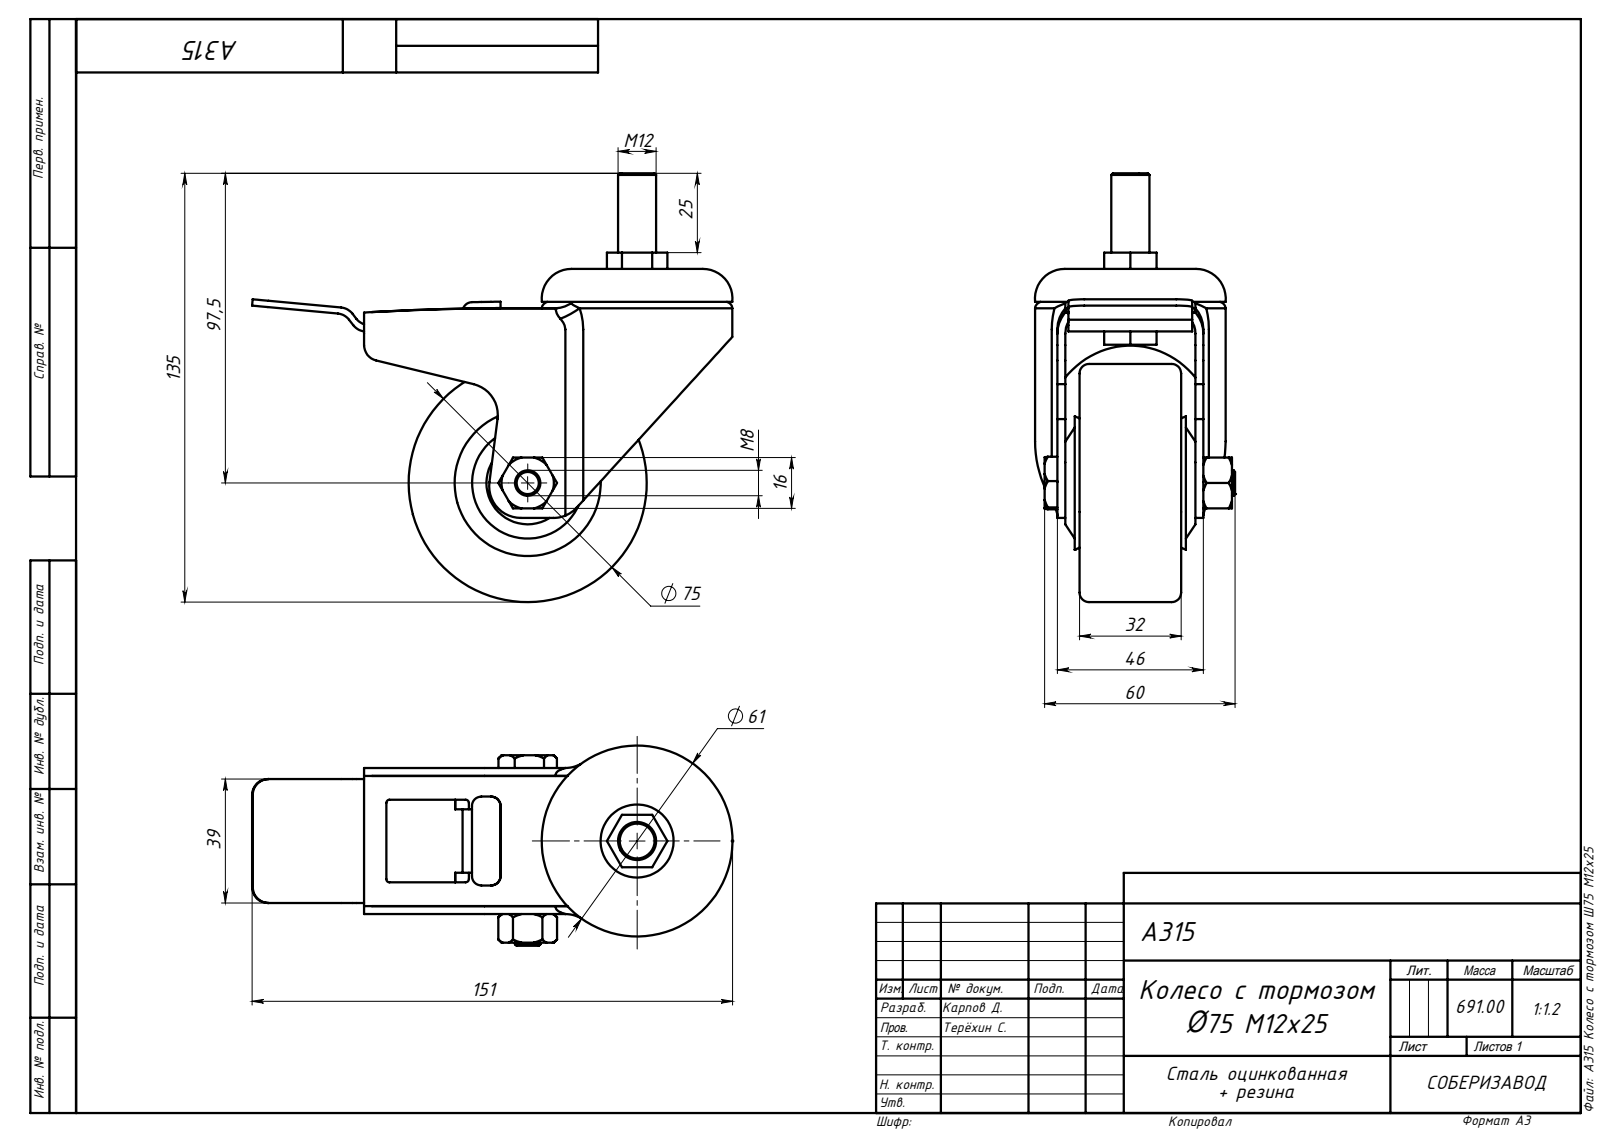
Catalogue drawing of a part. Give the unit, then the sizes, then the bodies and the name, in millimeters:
Units: millimetres
Overall size (bounding box): 151.33 × 135.03 × 63.05
Round holes (diameter × count): ⌀10 ×2, ⌀6 ×1, ⌀8 ×1, ⌀34 ×1
Round bosses / shafts (diameter × count): ⌀75 ×1, ⌀38 ×1, ⌀12 ×1
Partial cylindrical surfaces — rounded edges, fillets, slot ends (radius × count): R5 ×7, R10 ×7, R3 ×5, R1 ×4, R2 ×2, R27.5 ×1, R30 ×1, R804.01 ×1
Main face-to-face distances: 4.5, 39, 2.5, 36.5, 7, 43.5, 2, 41, 26, 46
Volume: 196 822 mm³ · Surface area: 80 662 mm²
Bodies: 12 solids, 378 faces (181 planar, 71 cylindrical, 126 other)
Part name (STEP PRODUCT): Болт_00; Колесо_00; A315 Болт_00; Дно_00 (+6 more)
STEP written by: SolidWorks 2021 (AUTOMOTIVE_DESIGN)
